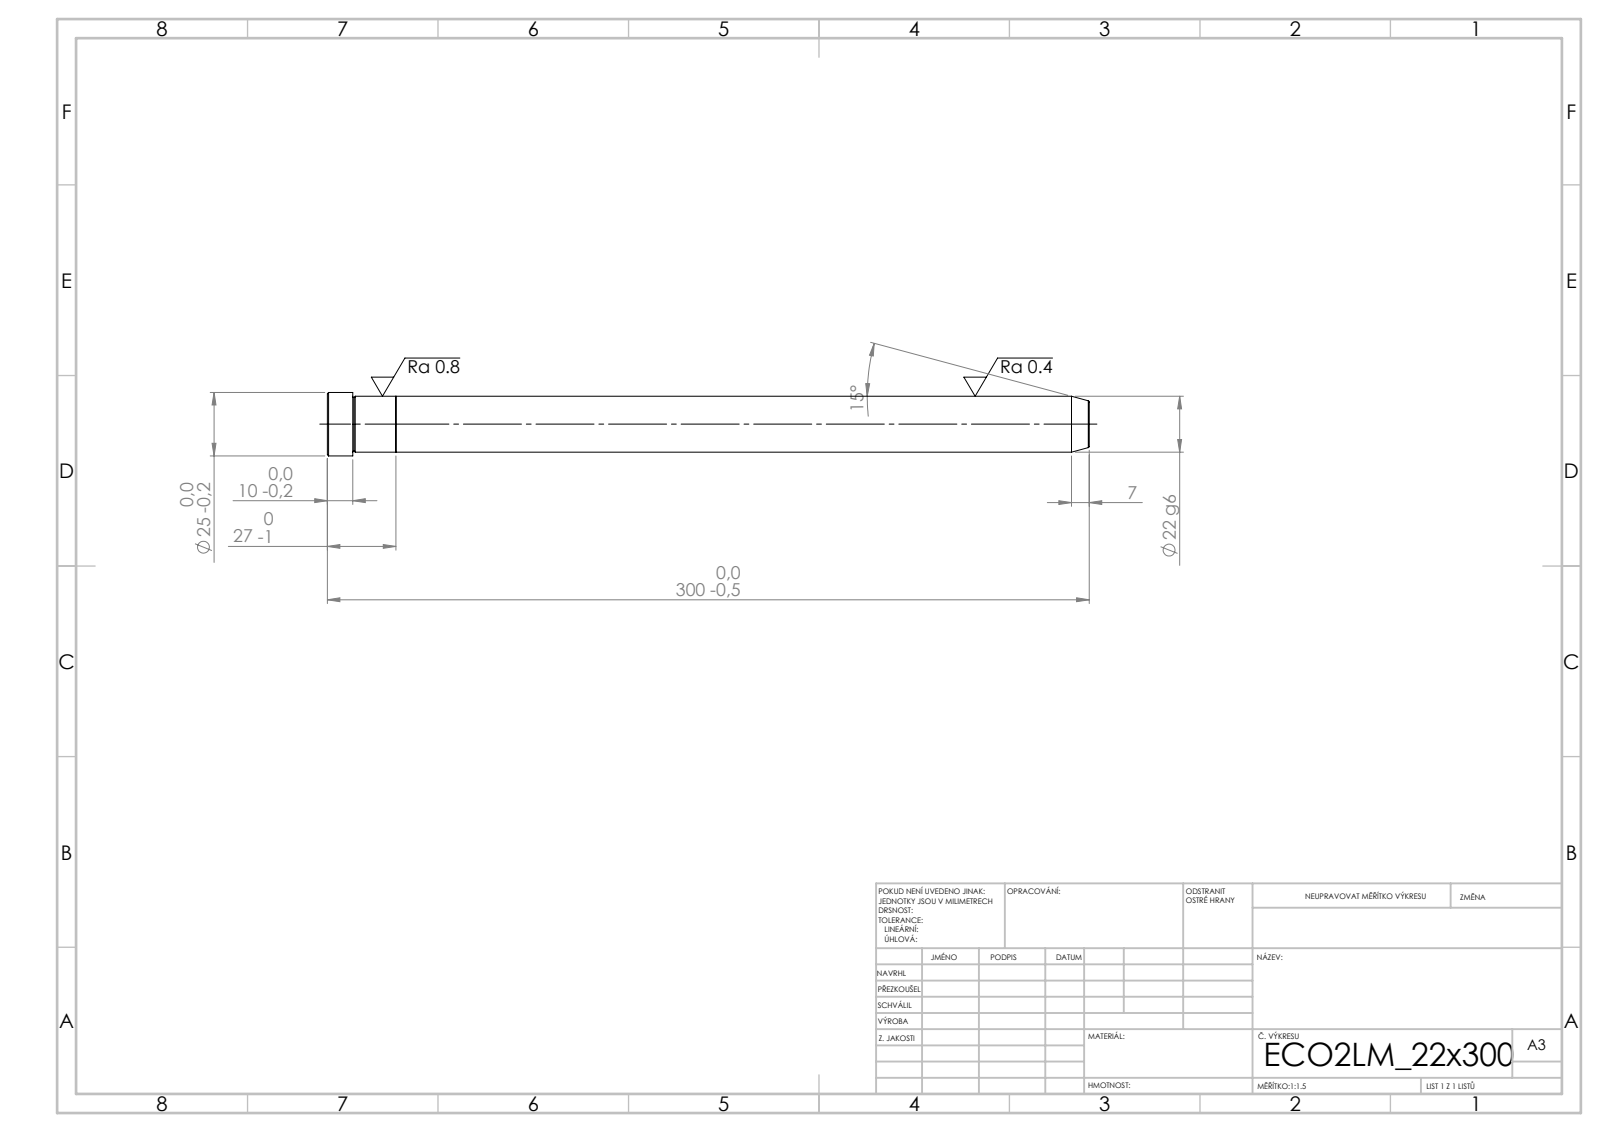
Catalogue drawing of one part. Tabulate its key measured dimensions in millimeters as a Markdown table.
| quantity | value |
| --- | --- |
| STEP written by | SolidWorks 2019 (CONFIG_CONTROL_DESIGN) |
| units | millimeters |
| bodies | 2 solids, 21 faces (5 planar, 6 cylindrical, 10 other) |
| overall size | 300 × 25 × 25 |
| volume | 114 681 mm³ |
| surface area | 22 433 mm² |
| round bosses / shafts (diameter × count) | 25 × 1, 22 × 1 |
| main face-to-face distances | 27, 273, 300, 290, 17, 10 |
